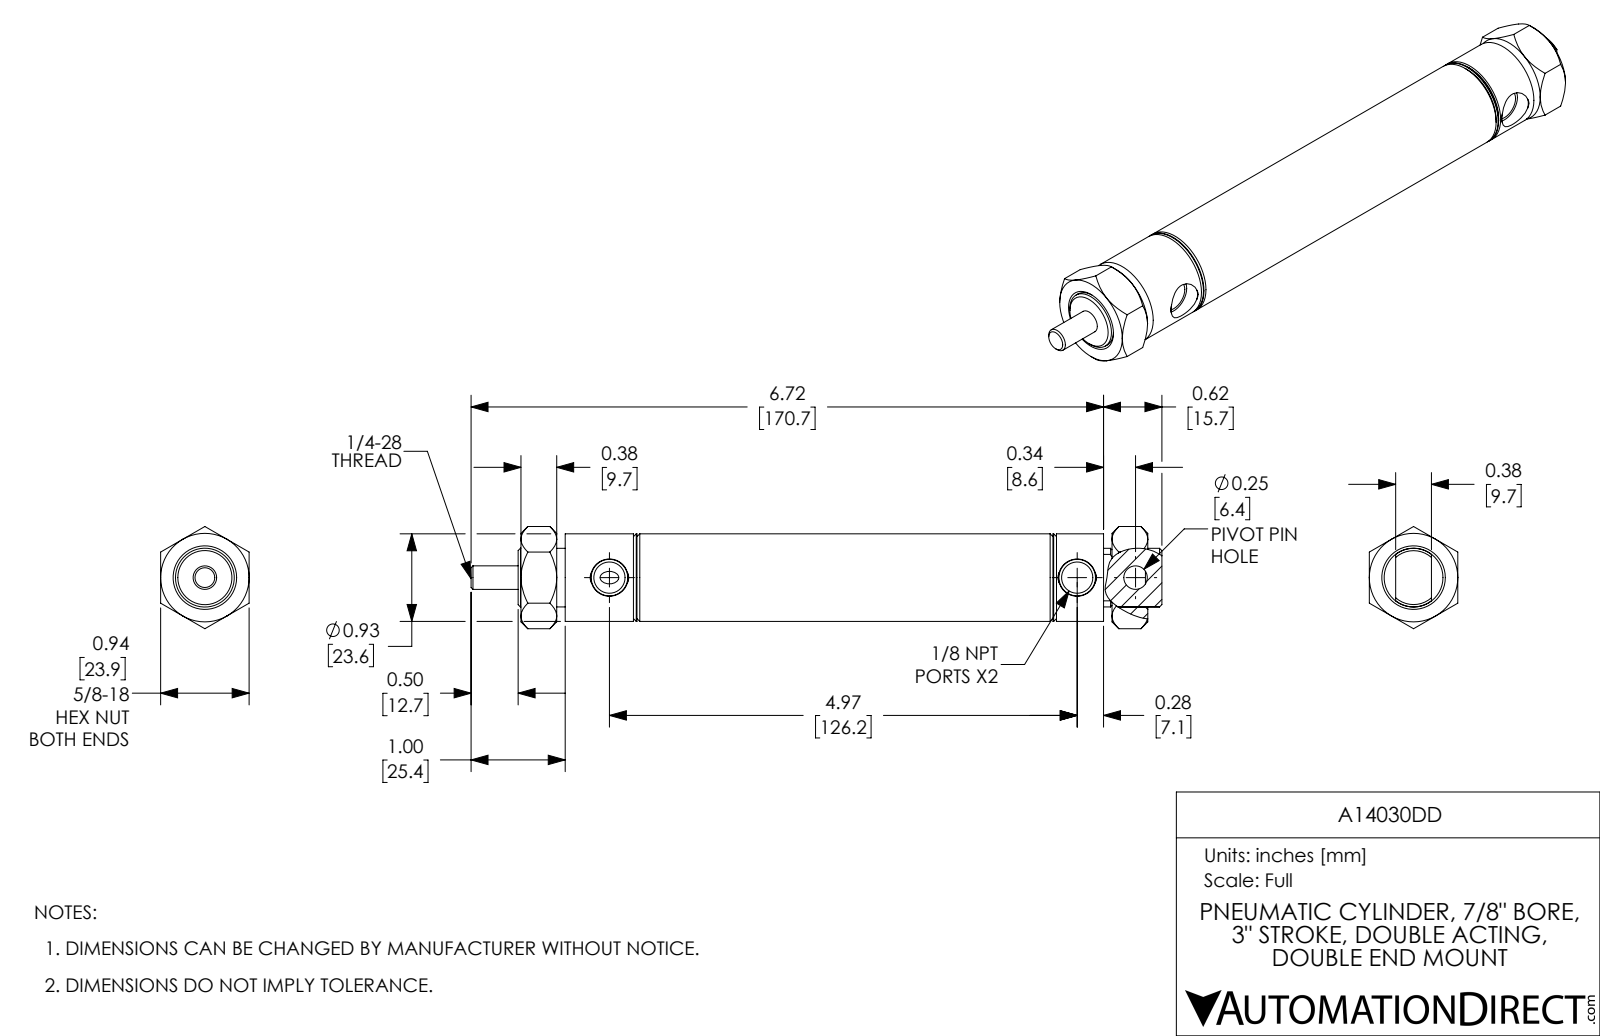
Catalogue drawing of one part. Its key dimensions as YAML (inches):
part_name: "A14030DD; A14030DD_Mounting Nut_D-9; A14030DD-Rod; A14030DD-MainBody"
step_written_by: "SolidWorks 2017 (AUTOMOTIVE_DESIGN)"
units: inches
bodies: {solids: 4, faces: 137, planar: 35, cylindrical: 38, other: 64}
overall_size: [7.34, 1.085, 0.94]
volume: 2.789
surface_area: 45.75
round_holes:
  - {diameter: 0.25, count: 2}
  - {diameter: 0.332, count: 2}
  - {diameter: 0.625, count: 1}
  - {diameter: 0.875, count: 1}
round_bosses_or_shafts:
  - {diameter: 0.93, count: 1}
  - {diameter: 0.623, count: 1}
  - {diameter: 0.562, count: 1}
face_to_face_distances: [0.94, 0.5, 0.47, 6.19, 0.38, 4.722, 3.5, 3, 0.998, 0.28]
hole_center_spacings: [0.62, 4.97, 5.59]
